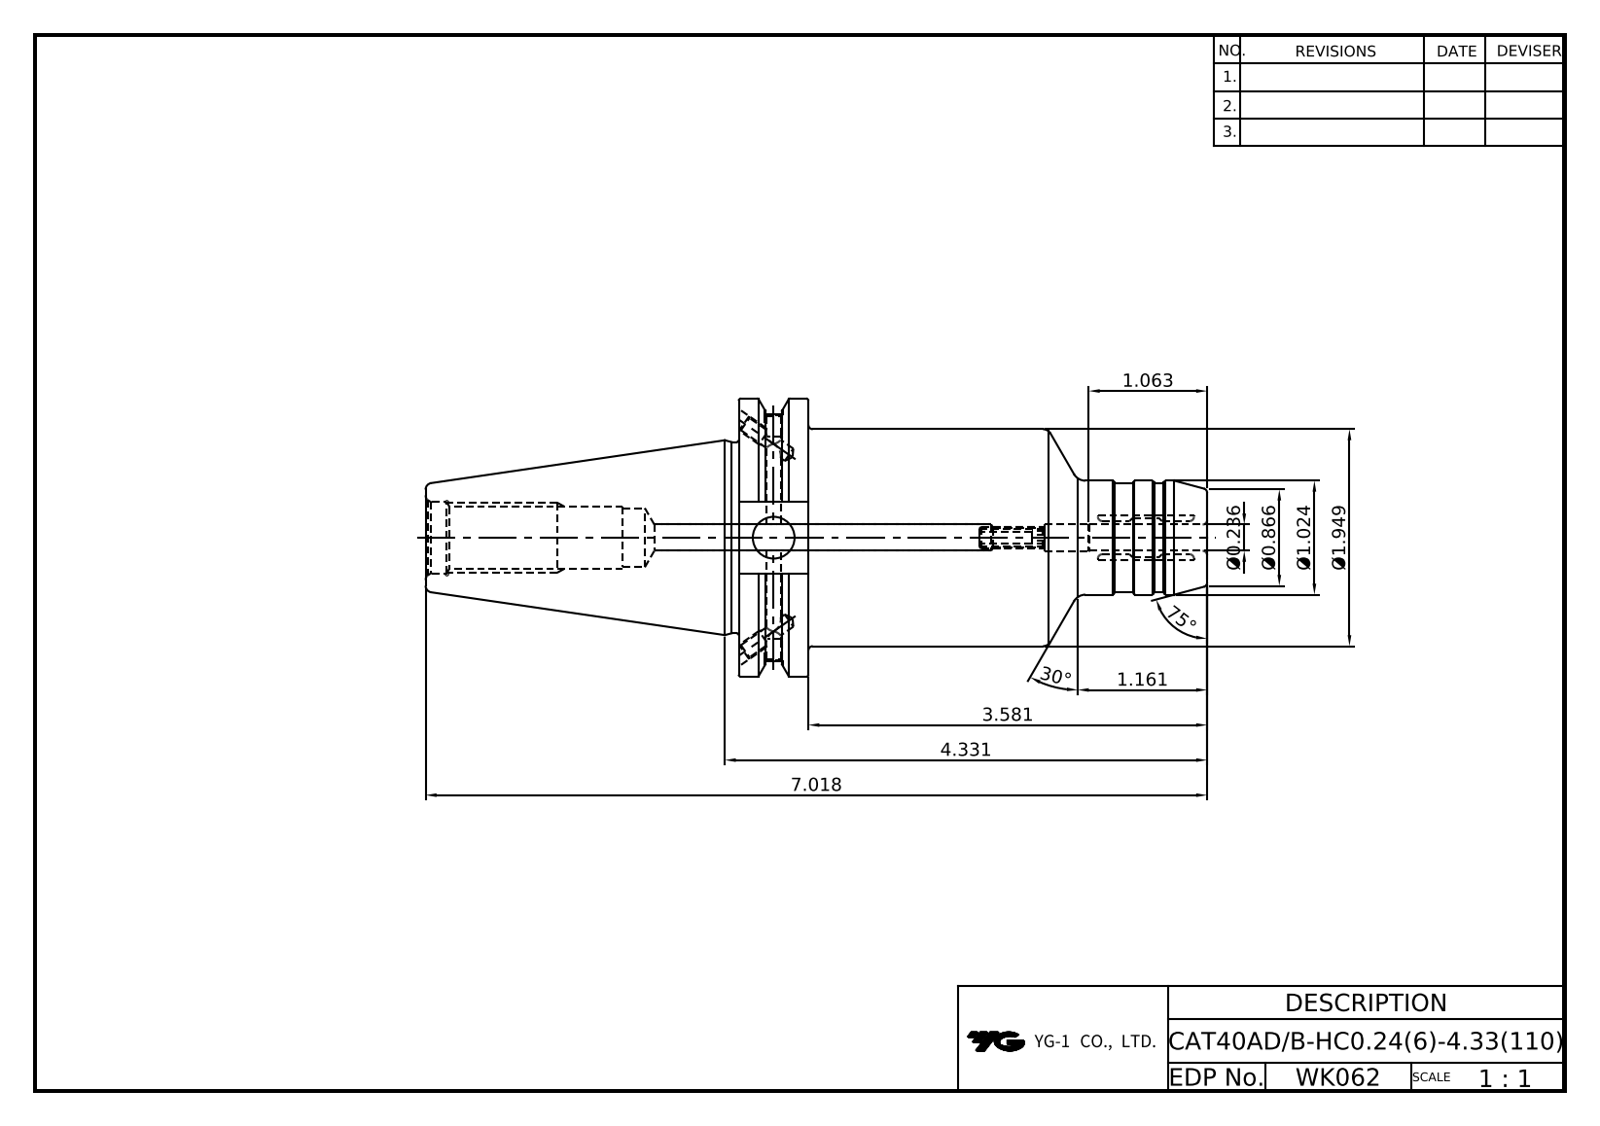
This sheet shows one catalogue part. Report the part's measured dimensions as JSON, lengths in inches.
{"part_name": "CAT40ADB-HC6-110", "step_written_by": "Autodesk Inventor 2020 (AUTOMOTIVE_DESIGN)", "units": "inches", "bodies": {"solids": 1, "faces": 112, "planar": 34, "cylindrical": 36, "other": 42}, "overall_size": [7.018, 2.5, 2.405], "volume_in3": 14.02, "surface_area_in2": 50.71, "round_holes": [[0.128, 4], [0.157, 2], [0.165, 2], [0.169, 1], [0.236, 1], [0.26, 1], [0.375, 1], [0.512, 1], [0.527, 1], [0.642, 1]], "round_bosses_or_shafts": [[2.5, 1], [1.949, 1], [1.717, 1], [1.024, 1], [0.984, 1]], "partial_cylinders_radius": [[0.322, 1], [1.108, 1]], "face_to_face_distances": [0.625, 4.206, 3.581, 1.874, 0.645, 2.812, 3.437, 7.018, 3.05, 0.238]}
